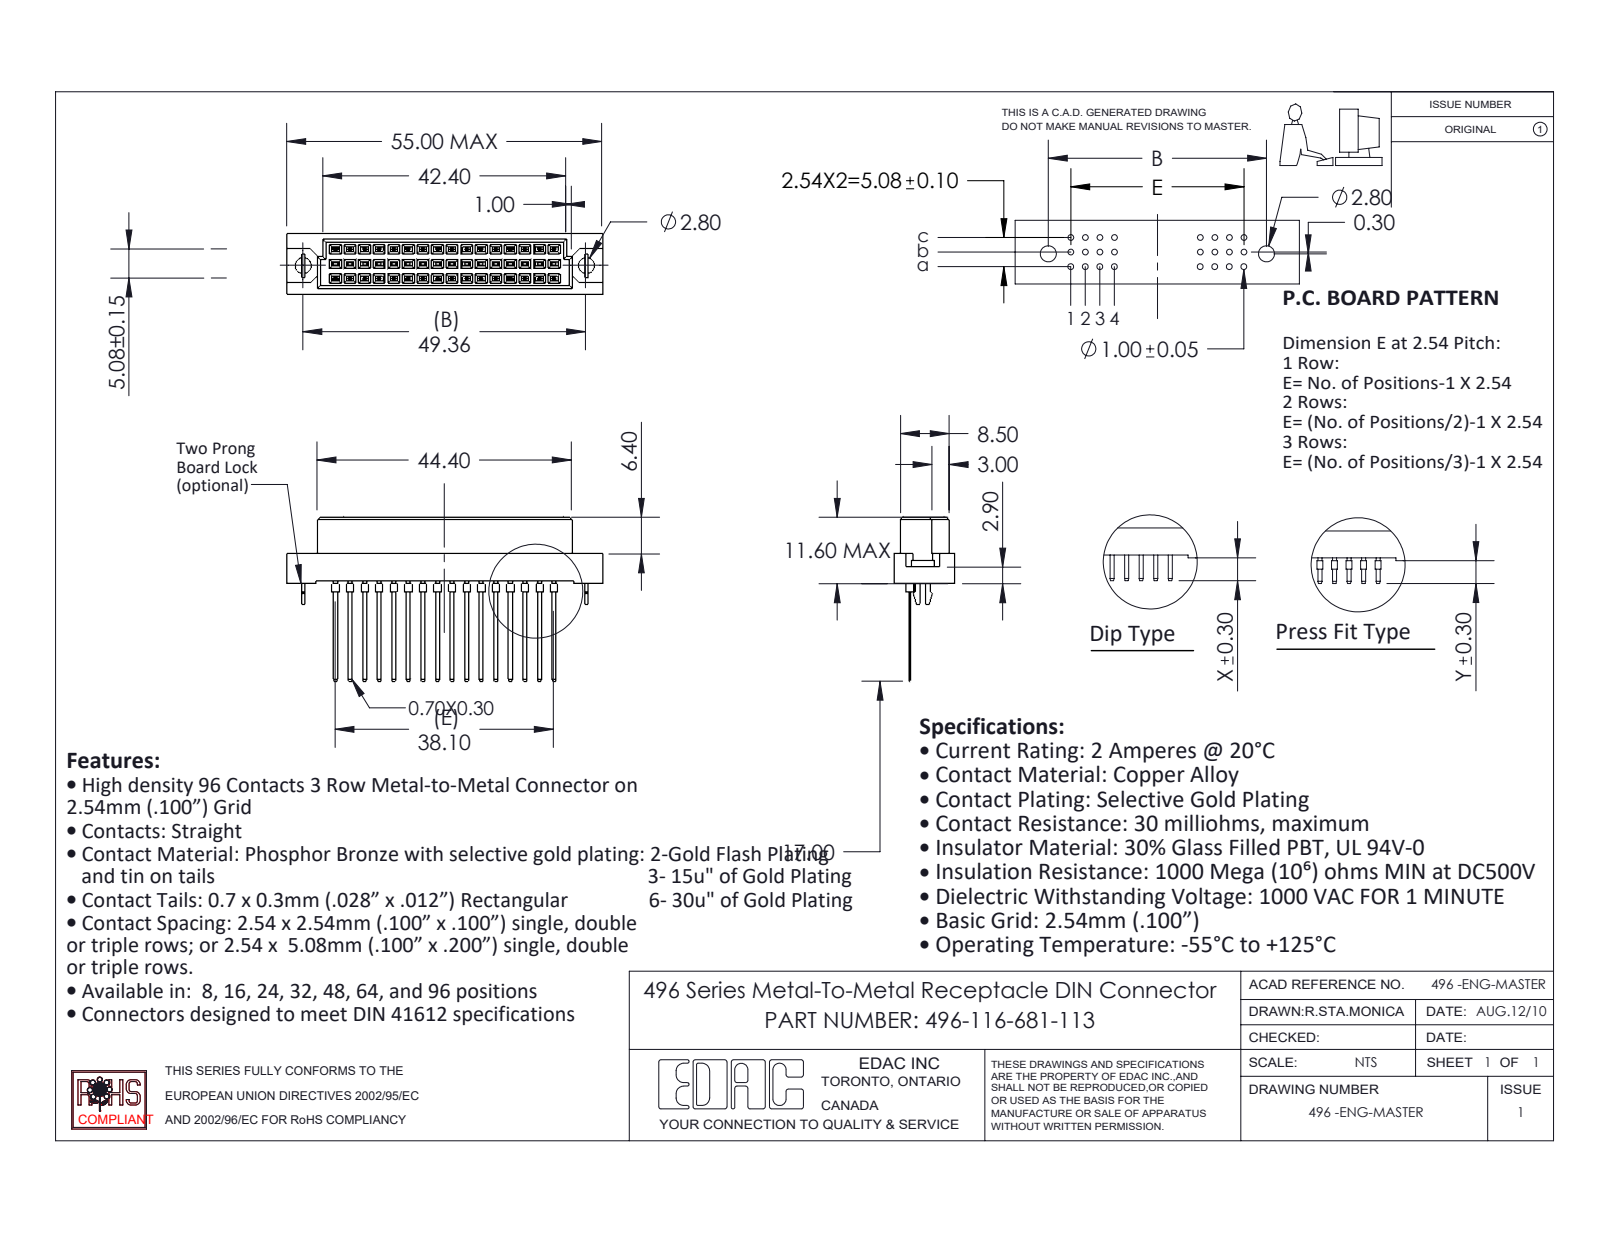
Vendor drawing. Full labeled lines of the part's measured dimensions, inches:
Part name (STEP PRODUCT): 496-116-681-113; 496 Part_48; 496-290_81; 496 Bore-lock
STEP written by: SolidWorks 2020 (CONFIG_CONTROL_DESIGN)
Units: inches
Bodies: 19 solids, 990 faces (952 planar, 38 cylindrical, 0 other)
Overall size (bounding box): 2.165 × 1.126 × 0.417
Volume: 0.287 in³ · Surface area: 7.848 in²
Round holes (diameter × count): ⌀0.11 ×2
Round bosses / shafts (diameter × count): ⌀0.039 ×16
Partial cylindrical surfaces — rounded edges, fillets, slot ends (radius × count): R0.021 ×1
Main face-to-face distances: 0.1, 0.041, 0.376, 0.2, 0.032, 0.073, 0.061, 0.115, 0.303, 0.103
Hole centre spacings: 1.943
